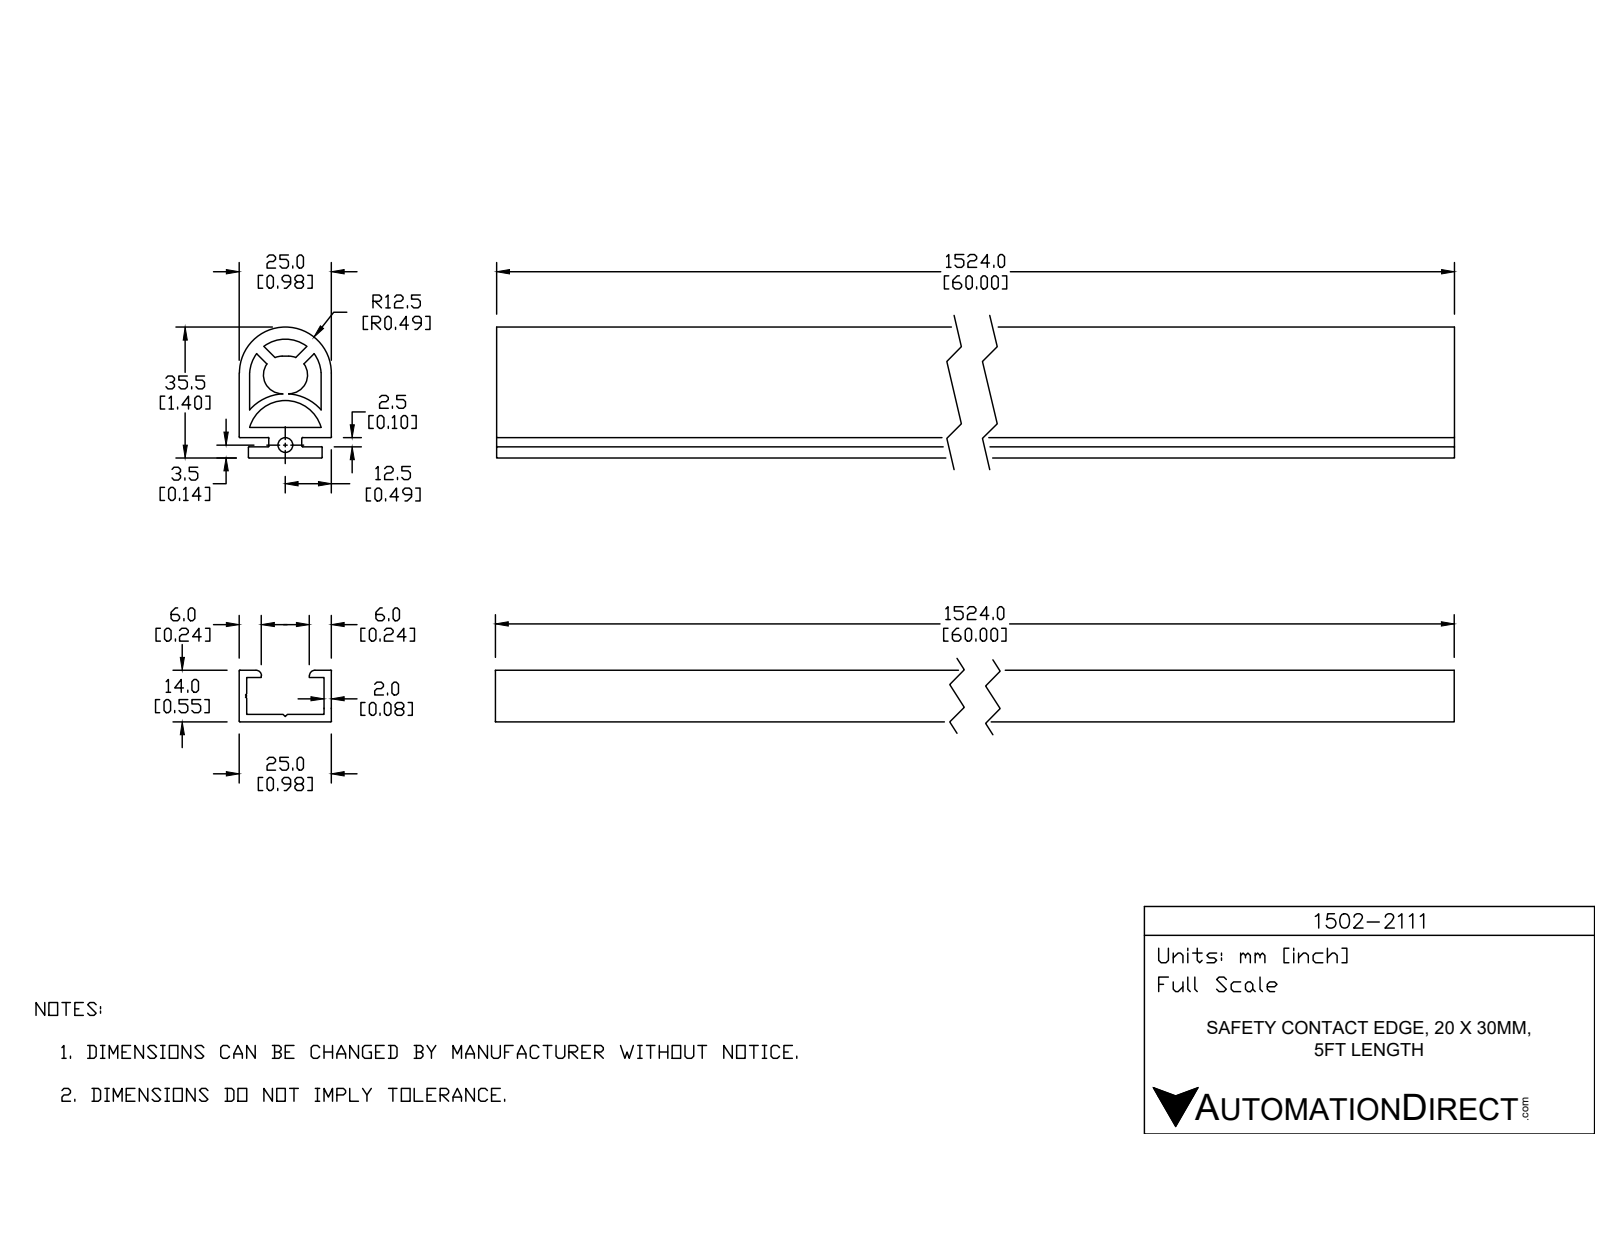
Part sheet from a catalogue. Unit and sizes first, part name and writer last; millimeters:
Units: millimetres
Overall size (bounding box): 609.6 × 35.5 × 25
Round holes (diameter × count): ⌀4 ×1
Partial cylindrical surfaces — rounded edges, fillets, slot ends (radius × count): R0.2 ×10, R5.12 ×2, R9.7 ×1, R10.11 ×1, R12.5 ×1, R12.9 ×1
Main face-to-face distances: 2.8, 5.5, 8.3, 25, 2.5, 3, 5.3, 2.85, 22.15, 22.2
Volume: 304 311 mm³ · Surface area: 182 651 mm²
Bodies: 1 solid, 47 faces (23 planar, 24 cylindrical, 0 other)
Part name (STEP PRODUCT): 1502-2111
STEP written by: SolidWorks 2017 (AUTOMOTIVE_DESIGN)
